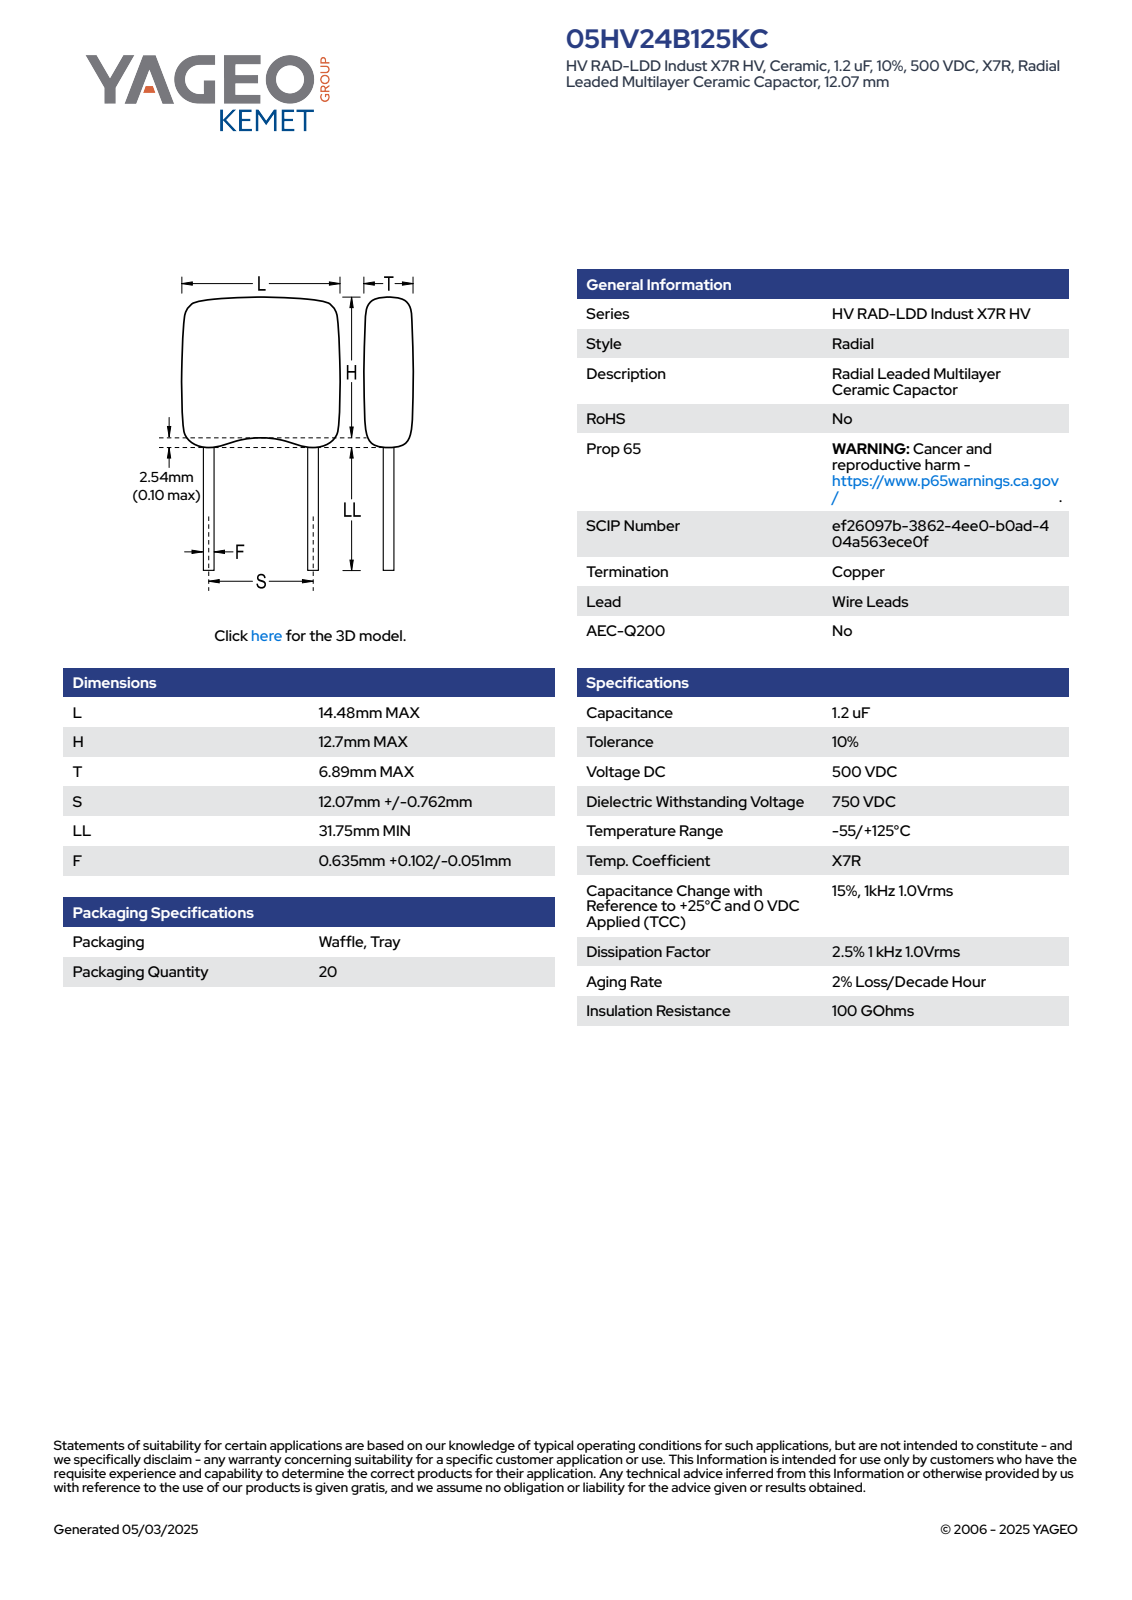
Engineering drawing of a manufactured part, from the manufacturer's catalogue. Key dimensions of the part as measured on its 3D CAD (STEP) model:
Part name (STEP PRODUCT): CCRM_RCST_HV24_L14.48H12.7T6.89S12.07LL3.175F0.737
STEP written by: SolidWorks 2021 (AUTOMOTIVE_DESIGN)
Units: millimetres
Bodies: 4 solids, 92 faces (66 planar, 16 cylindrical, 10 other)
Overall size (bounding box): 45.97 × 14.48 × 5.08
Volume: 966 mm³ · Surface area: 782 mm²
Round bosses / shafts (diameter × count): ⌀0.64 ×2
Partial cylindrical surfaces — rounded edges, fillets, slot ends (radius × count): R0.5 ×8, R2 ×4
Main face-to-face distances: 5.08, 14.48, 14.22, 31.75, 45.97, 40.15, 8.4, 5.82, 37.85, 6.1
